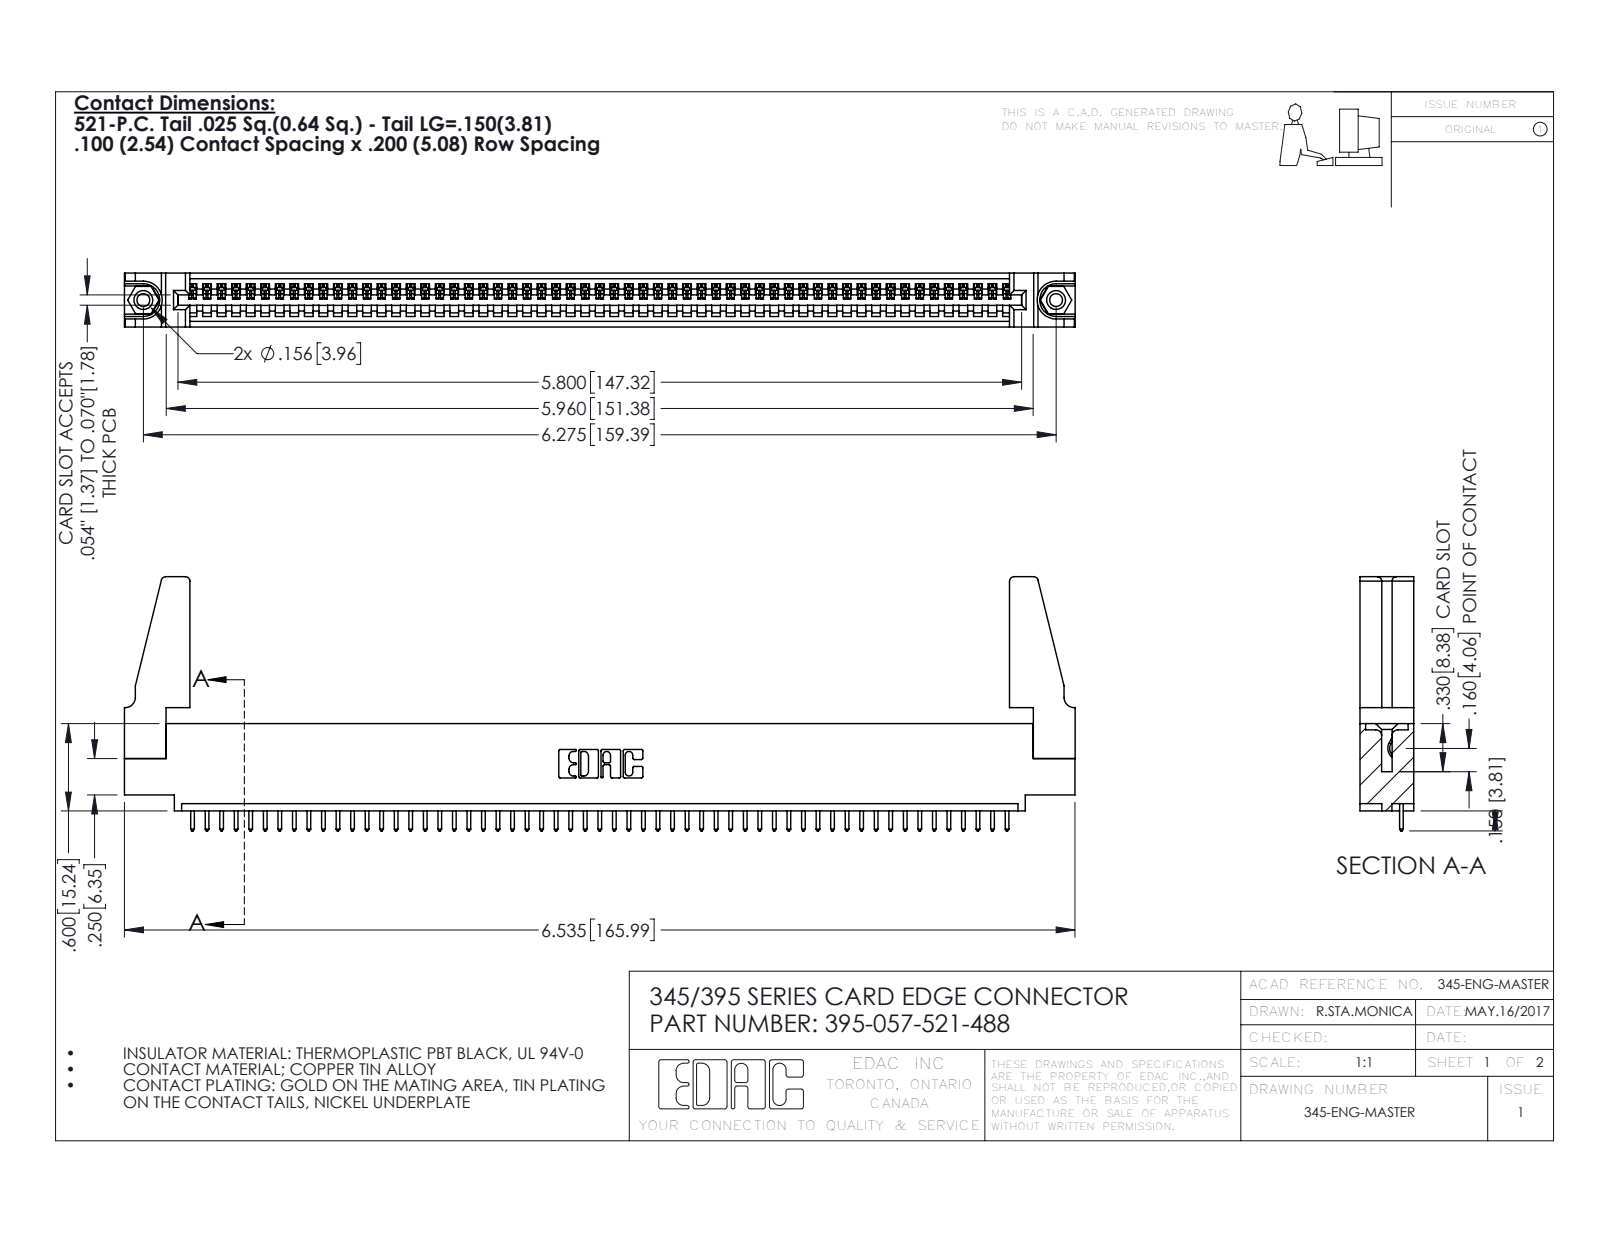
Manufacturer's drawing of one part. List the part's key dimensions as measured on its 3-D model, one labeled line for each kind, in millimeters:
Part name (STEP PRODUCT): 395-057-521-488; 345-250-001_345-250-001-102; 345 Part_0.110 Offset - 0.156 Dia-TH; 345-292-001_345-293-121 (+1 more)
STEP written by: SolidWorks 2016 (CONFIG_CONTROL_DESIGN)
Units: millimetres
Bodies: 62 solids, 3560 faces (2436 planar, 1108 cylindrical, 16 other)
Overall size (bounding box): 166 × 44.4 × 9.4
Volume: 18 910 mm³ · Surface area: 23 590 mm²
Round holes (diameter × count): ⌀2.3 ×2, ⌀3.2 ×2, ⌀4 ×2, ⌀1.6 ×1
Round bosses / shafts (diameter × count): ⌀3.9 ×2
Partial cylindrical surfaces — rounded edges, fillets, slot ends (radius × count): R0.2 ×114, R0.3 ×114, R0.3 ×22, R0.8 ×8, R0.2 ×6, R0.8 ×6, R0.7 ×3, R0.8 ×2
Main face-to-face distances: 1.8, 7.6, 9.4, 5.1, 2.5, 6.9, 0.6, 5.7, 3.8, 1.8
Hole centre spacings: 6.9, 153.4, 159.4
